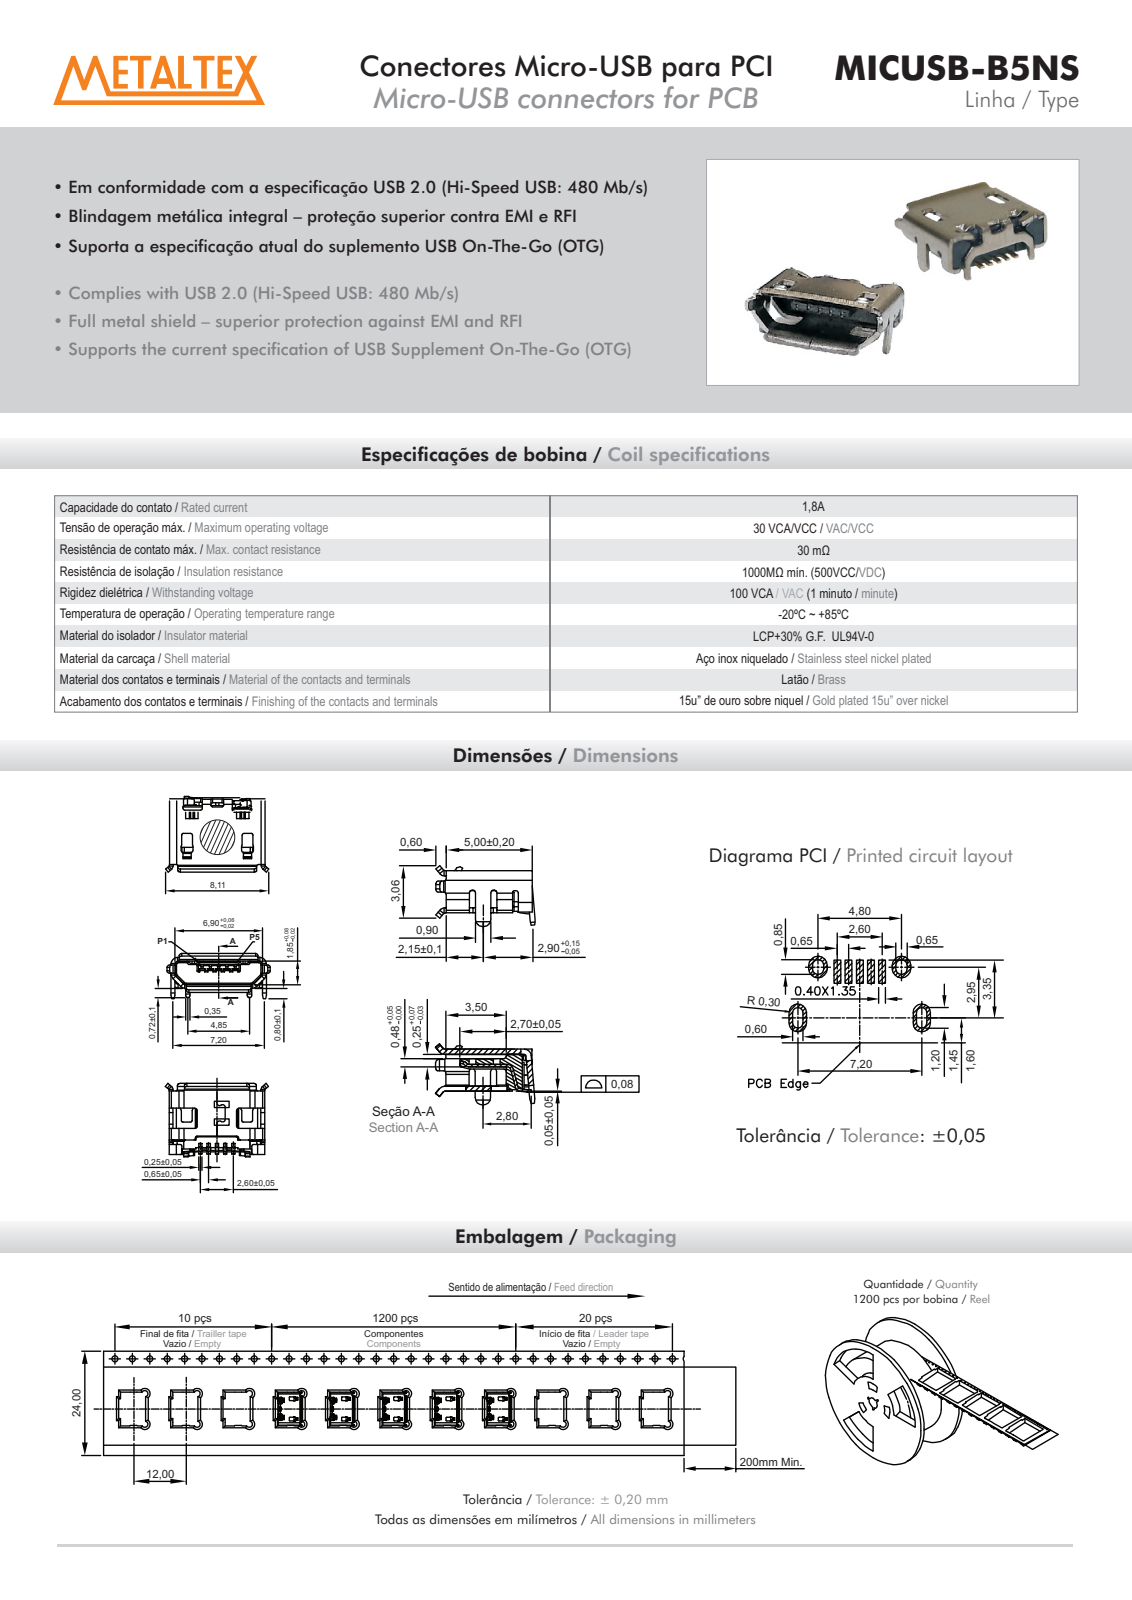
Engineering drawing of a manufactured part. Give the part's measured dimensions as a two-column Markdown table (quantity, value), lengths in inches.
| quantity | value |
| --- | --- |
| part name | shell; md; 10336105A026 |
| STEP written by | CoCreate Modeling 17.0 01-Apr-2010 (C) Parametric Technology GmbH (AUTOMOTIVE_DESIGN) |
| units | inches |
| bodies | 2 solids, 651 faces (414 planar, 205 cylindrical, 32 other) |
| overall size | 0.319 × 0.239 × 0.144 |
| volume | 0.003 in³ |
| surface area | 0.437 in² |
| partial cylindrical surfaces (radius × count) | 0.005 × 42, 0.004 × 32, 0.008 × 18, 0.006 × 14, 0.016 × 14, 0.01 × 11, 0.012 × 11, 0.022 × 9 |
| main face-to-face distances | 0.085, 0.073, 0.097, 0.022, 0.283, 0.037, 0.059, 0.085, 0.014, 0.035 |
